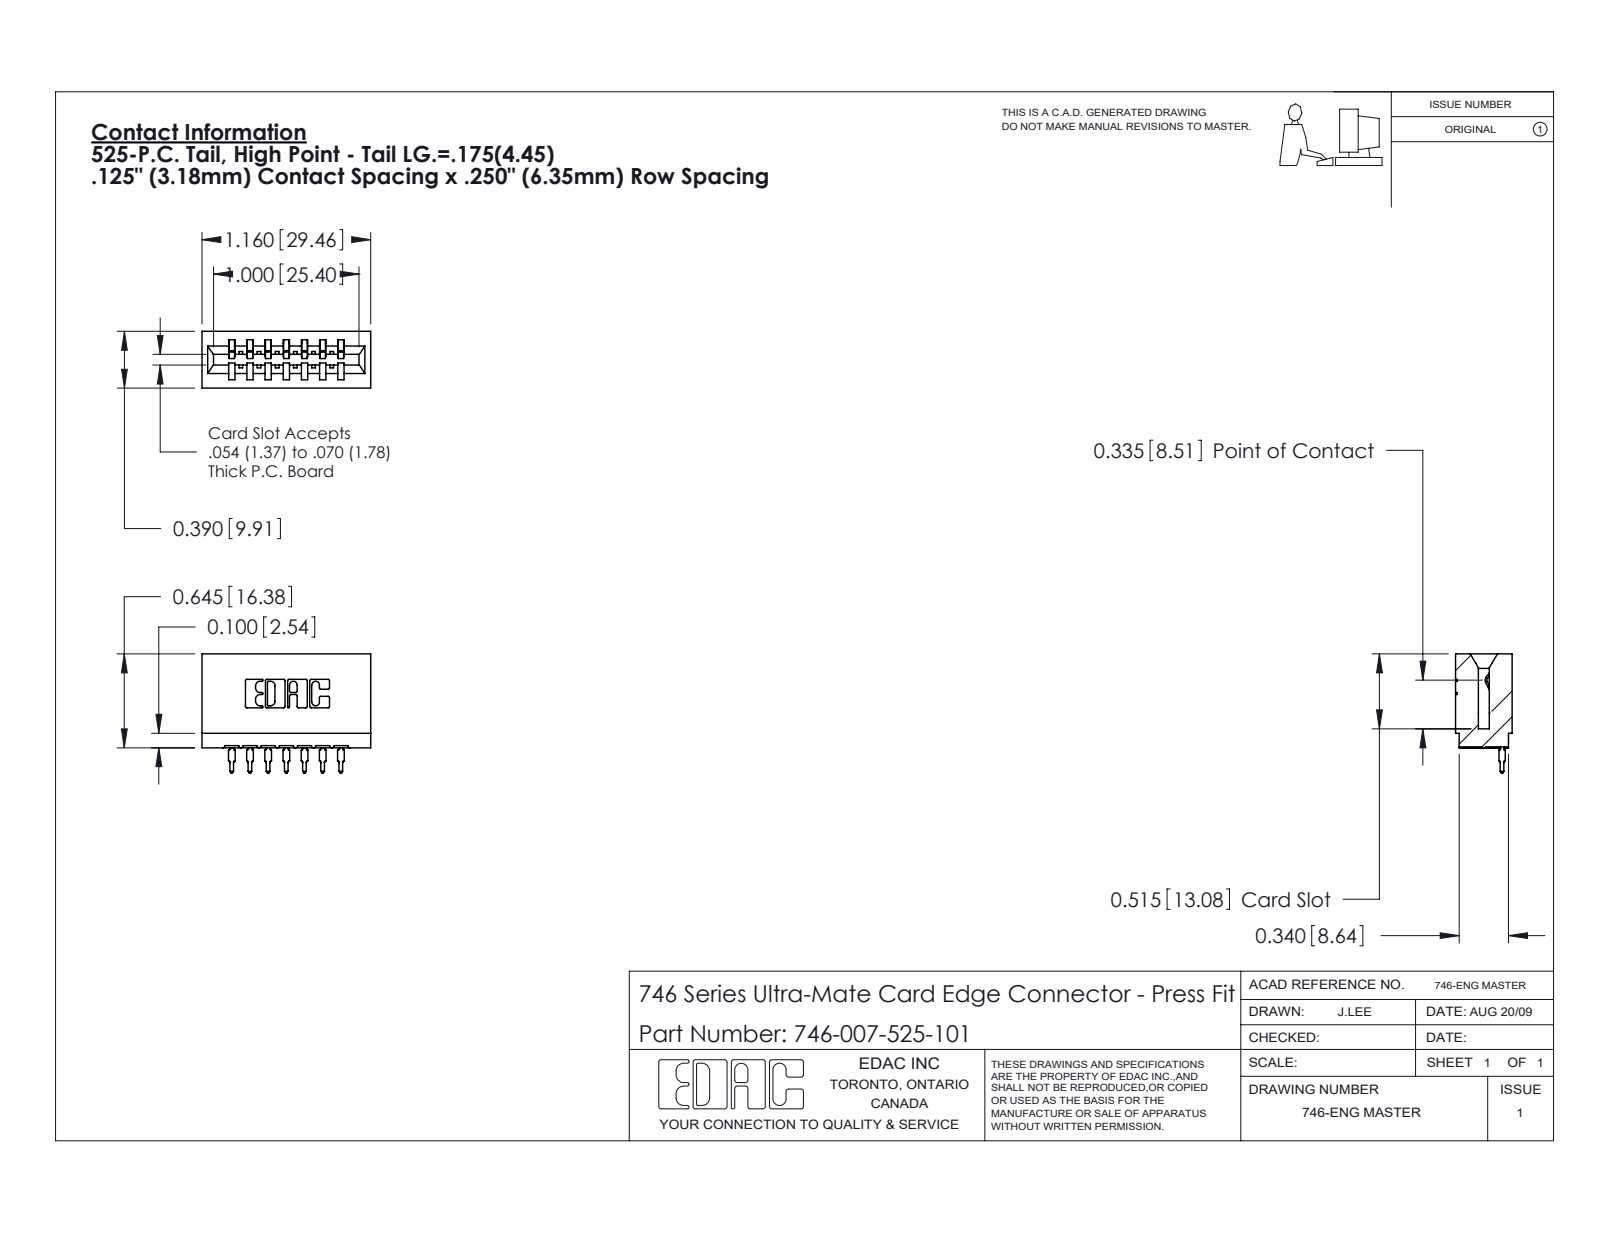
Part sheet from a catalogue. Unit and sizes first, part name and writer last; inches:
Units: inches
Overall size (bounding box): 1.16 × 0.819 × 0.39
Partial cylindrical surfaces — rounded edges, fillets, slot ends (radius × count): R0.01 ×22, R0.021 ×14, R0.015 ×8, R0.007 ×6, R0.031 ×6, R0.005 ×4, R0.011 ×4, R0.026 ×3
Main face-to-face distances: 0.25, 0.042, 0.333, 0.125, 0.5, 0.125, 0.057, 0.292, 0.208, 0.39
Volume: 0.202 in³ · Surface area: 6.636 in²
Bodies: 8 solids, 853 faces (496 planar, 175 cylindrical, 182 other)
Part name (STEP PRODUCT): 746-292-001_525; 746-007-525-101; 746 Part_.515 Slot Depth - 01
STEP written by: SolidWorks 2020 (CONFIG_CONTROL_DESIGN)
